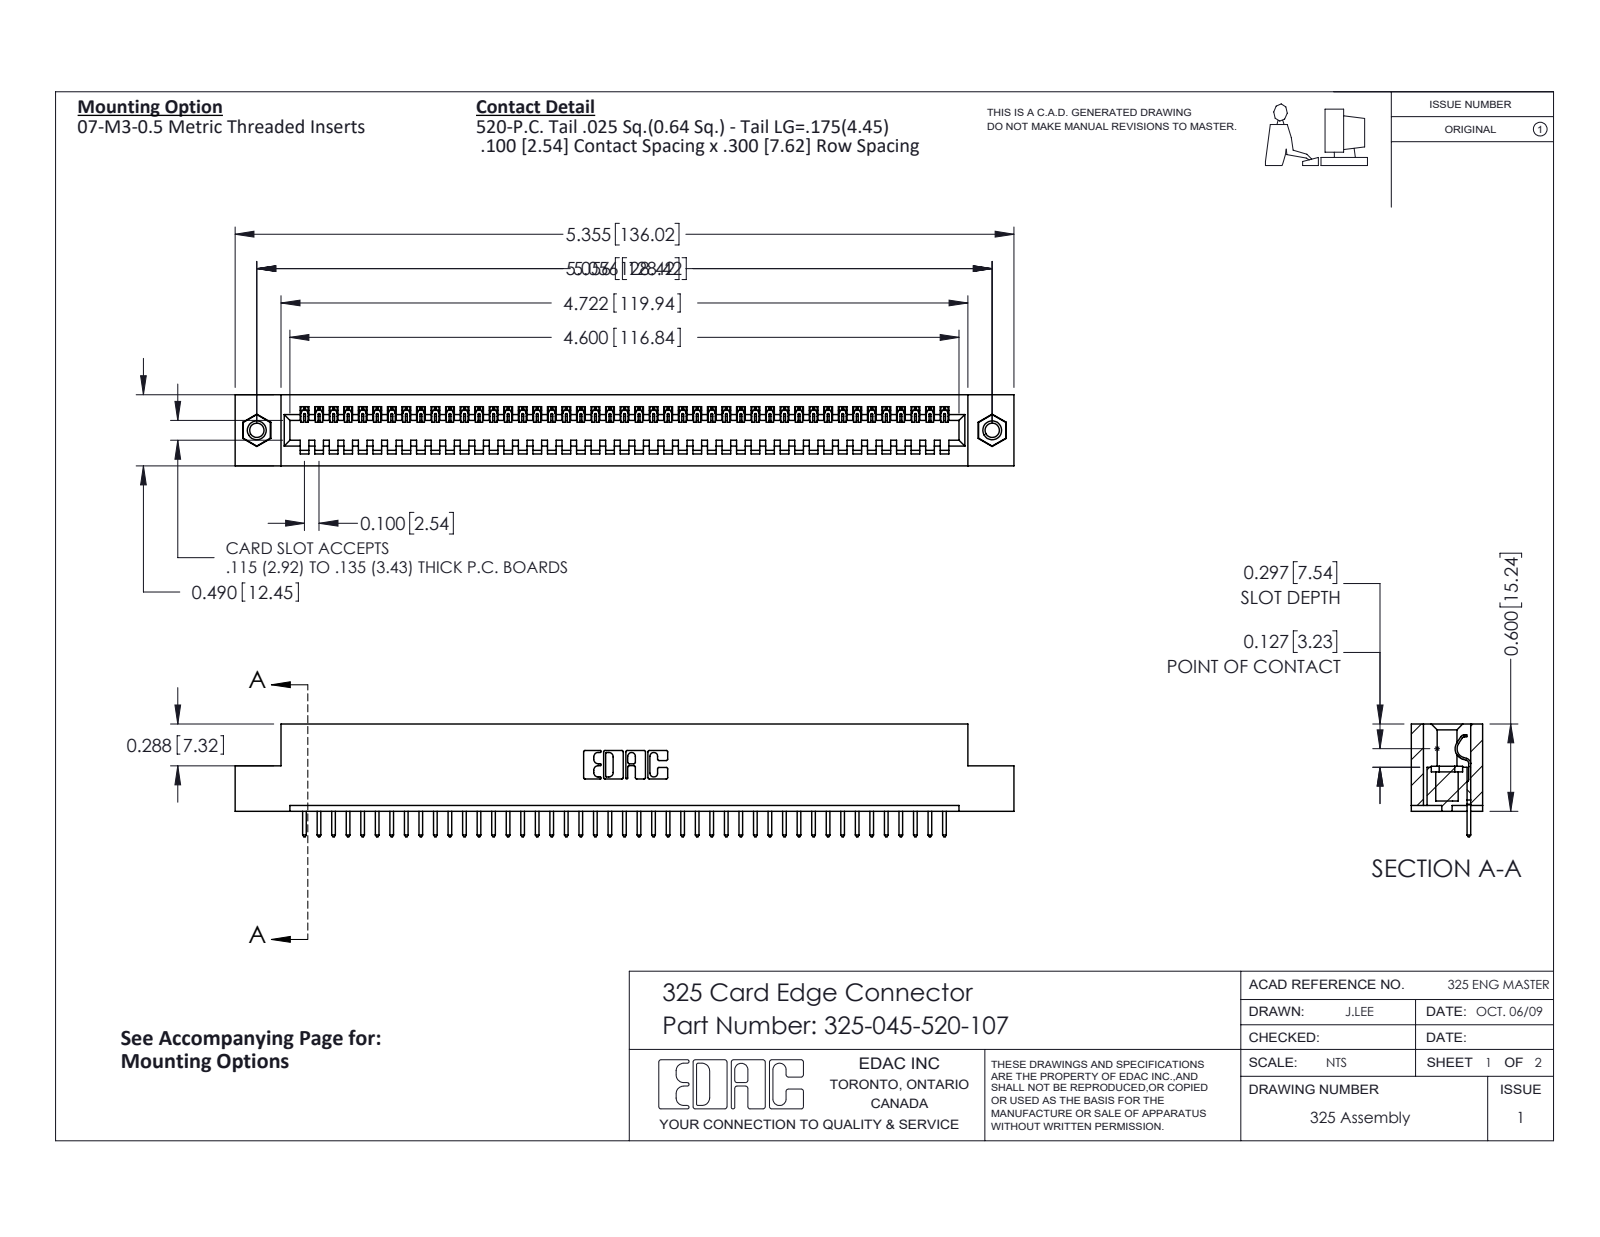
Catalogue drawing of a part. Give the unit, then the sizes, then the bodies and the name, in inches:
Units: inches
Overall size (bounding box): 5.355 × 0.775 × 0.49
Round holes (diameter × count): ⌀0.098 ×2, ⌀0.125 ×2, ⌀0.16 ×2
Round bosses / shafts (diameter × count): ⌀0.155 ×2
Partial cylindrical surfaces — rounded edges, fillets, slot ends (radius × count): R0.006 ×90, R0.01 ×90, R0.01 ×22, R0.007 ×6, R0.031 ×6, R0.026 ×3, R0.014 ×1, R0.022 ×1
Main face-to-face distances: 0.083, 0.407, 0.49, 0.3, 0.107, 0.383, 0.025, 0.325, 0.56, 0.263
Hole centre spacings: 5.056
Volume: 1.047 in³ · Surface area: 28.45 in²
Bodies: 48 solids, 2784 faces (1992 planar, 776 cylindrical, 16 other)
Part name (STEP PRODUCT): 345-250-001_345-250-005-103; 325 Part_TI; 325-292-001_325-293-120; 325-045-520-107
STEP written by: SolidWorks 2016 (CONFIG_CONTROL_DESIGN)
